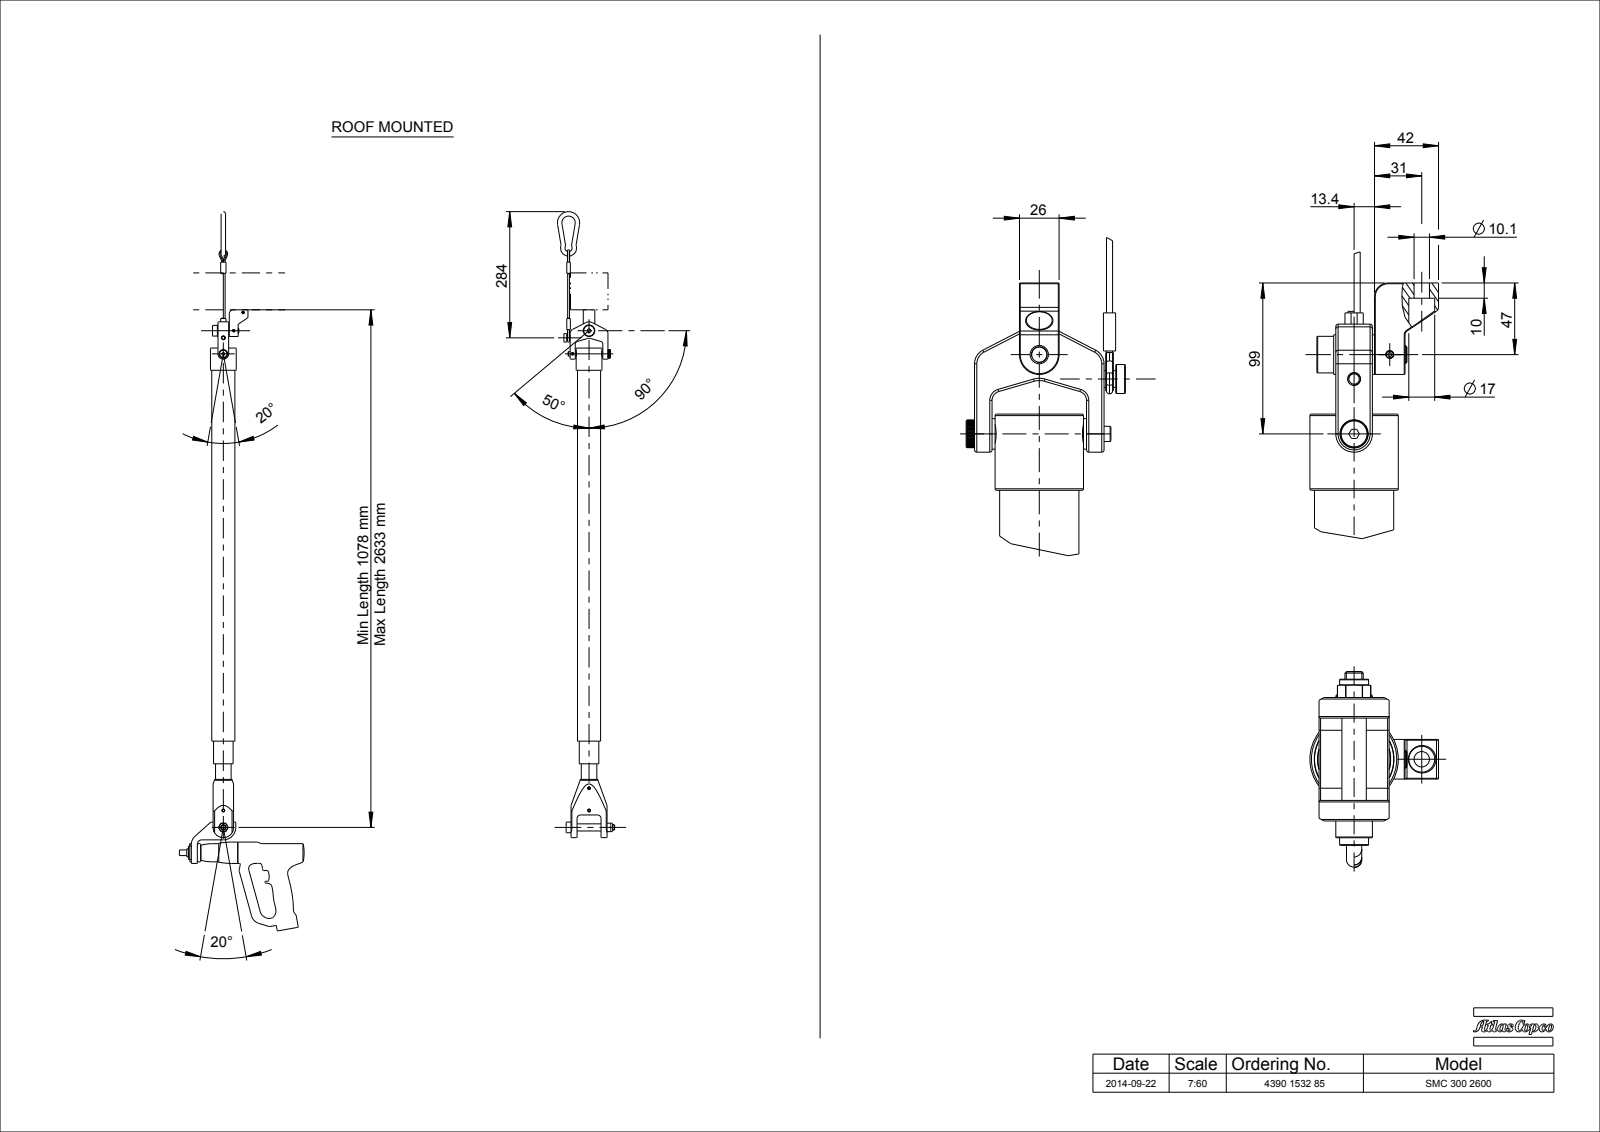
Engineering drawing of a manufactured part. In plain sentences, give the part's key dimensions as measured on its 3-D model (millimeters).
The part is named "4390152600; 4390152601; 4390152603; 4390152202 (+8 more)". Its 3-D file was written by "PRO/ENGINEER BY PARAMETRIC TECHNOLOGY CORPORATION, 2013410 (CONFIG_CONTROL_DESIGN)". It is 25 solids with 894 faces: 352 planar, 346 cylindrical and 196 other. Overall it measures 1407.8 by 128.6 by 84.4 millimeters. Its volume is 1 189 000 cubic millimeters and its surface area 841 632 square millimeters. Round holes: 5 of diameter 5, 3 of diameter 4.2, 3 of diameter 12, 2 of diameter 5.4, 2 of diameter 6, 2 of diameter 16, 1 of diameter 3, 1 of diameter 3.6, 1 of diameter 6.8, 1 of diameter 8, 1 of diameter 8.1, 1 of diameter 8.5. Round bosses or shafts: 6 of diameter 4, 4 of diameter 10, 2 of diameter 24, 2 of diameter 19, 2 of diameter 3.5, 1 of diameter 58, 1 of diameter 52, 1 of diameter 47.95. Partial cylindrical surfaces (rounded edges, fillets, slot ends): 16 of radius 1.5, 11 of radius 0.5, 6 of radius 0.2, 6 of radius 1, 2 of radius 2.5, 2 of radius 3, 2 of radius 4, 2 of radius 6. The main face-to-face distances are 11, 35, 46, 13.5, 40, 2, 24, 14, 27.5, 67.5. The hole center spacings are 28.35, 35, 36, 38, 44.4, 46.07, 50, 57.02.
